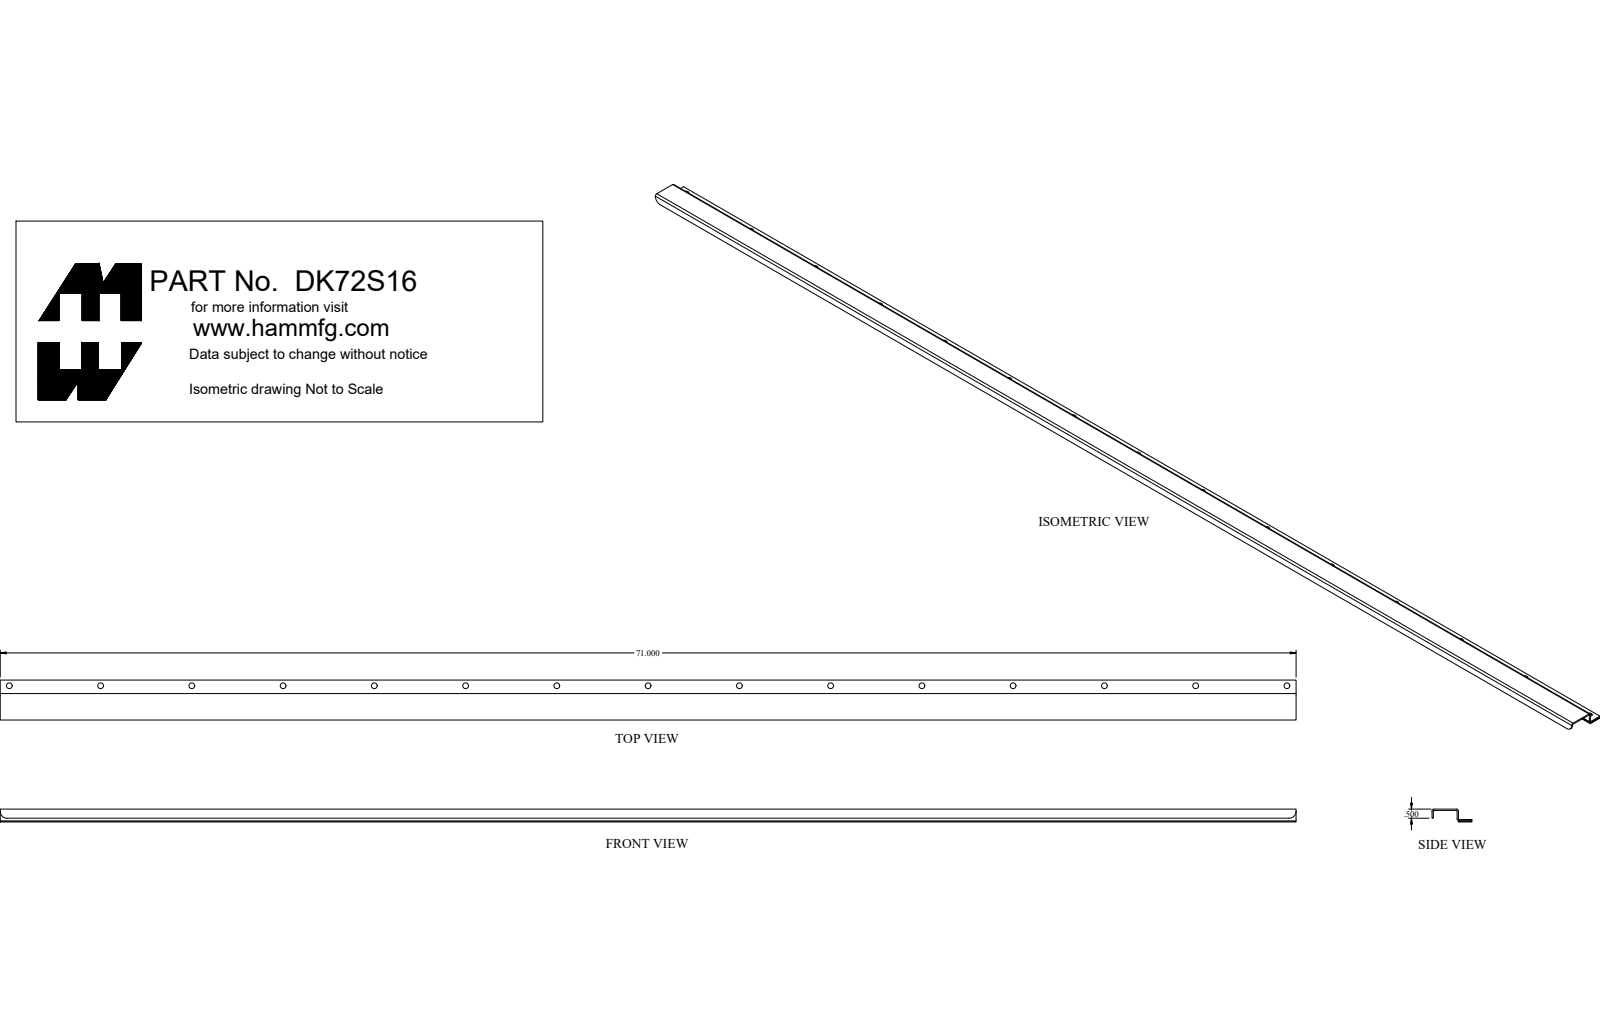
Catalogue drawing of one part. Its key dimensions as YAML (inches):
part_name: "DK72S16"
step_written_by: "SolidWorks 2021 (AUTOMOTIVE_DESIGN)"
units: inches
bodies: {solids: 5, faces: 76, planar: 47, cylindrical: 28, other: 1}
overall_size: [71, 2.188, 1.322]
volume: 19.17
surface_area: 566.9
round_holes:
  - {diameter: 0.313, count: 15}
  - {diameter: 0.196, count: 1}
  - {diameter: 0.275, count: 1}
round_bosses_or_shafts:
  - {diameter: 0.625, count: 1}
  - {diameter: 0.483, count: 1}
  - {diameter: 0.25, count: 1}
partial_cylinders:
  - {radius: 0.036, count: 3}
  - {radius: 0.108, count: 3}
  - {radius: 0.375, count: 2}
face_to_face_distances: [0.072, 0.572, 0.644, 0.063, 1.376, 0.5, 0.635, 0.707, 0.135, 1.448]
hole_center_spacings: [5, 10, 15, 20, 25, 30, 35, 40]
